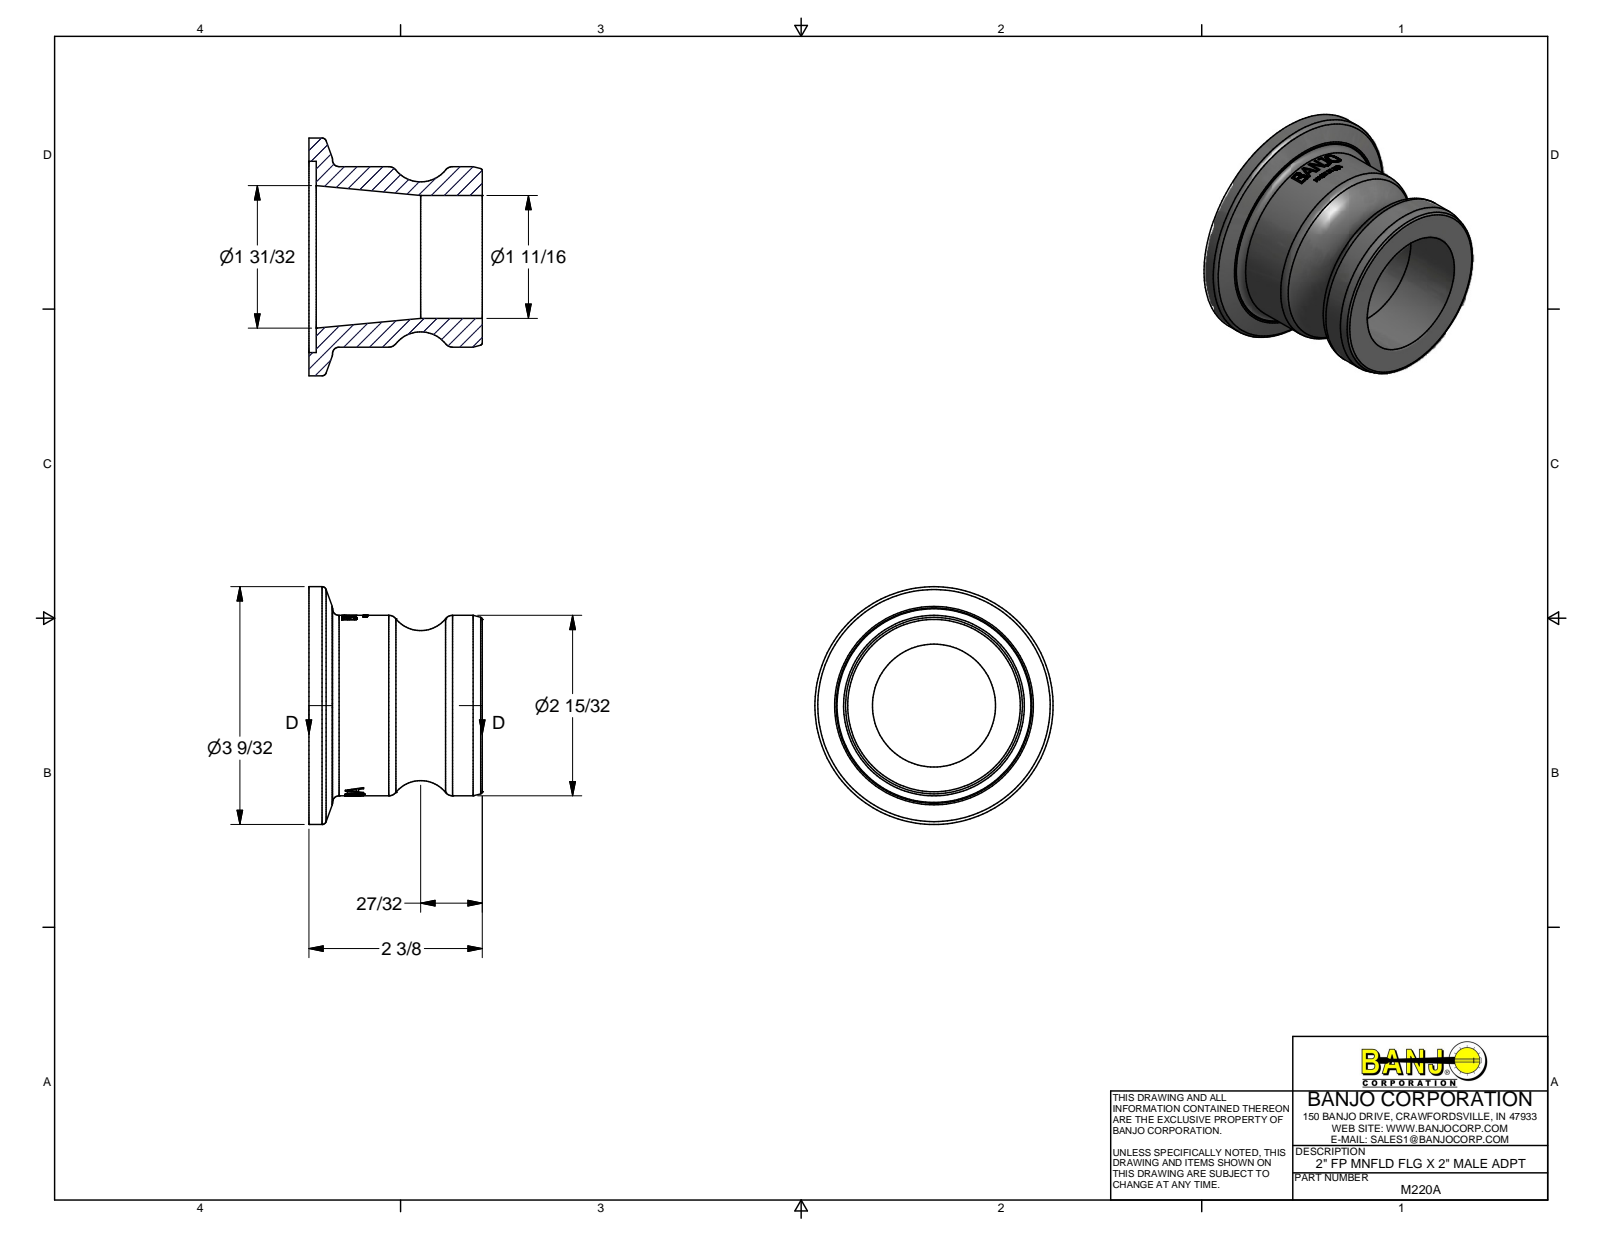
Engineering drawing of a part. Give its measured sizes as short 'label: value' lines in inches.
name: M220A
written by: Autodesk Inventor 2013 (AUTOMOTIVE_DESIGN)
unit: in
bodies: 1 solid, 306 faces (163 planar, 34 cylindrical, 109 other)
size: 3.27 × 3.27 × 2.38
volume: 5.509 in³; area: 43.26 in²
holes: 1× ⌀1.69, 1× ⌀2.63
bosses: 1× ⌀3.27, 1× ⌀2.482
rounds: 1× R1.231
face distances: 0.1, 2.38, 2.28, 0.324, 0.224, 2.056, 0.65, 0.75, 0.426, 1.63
